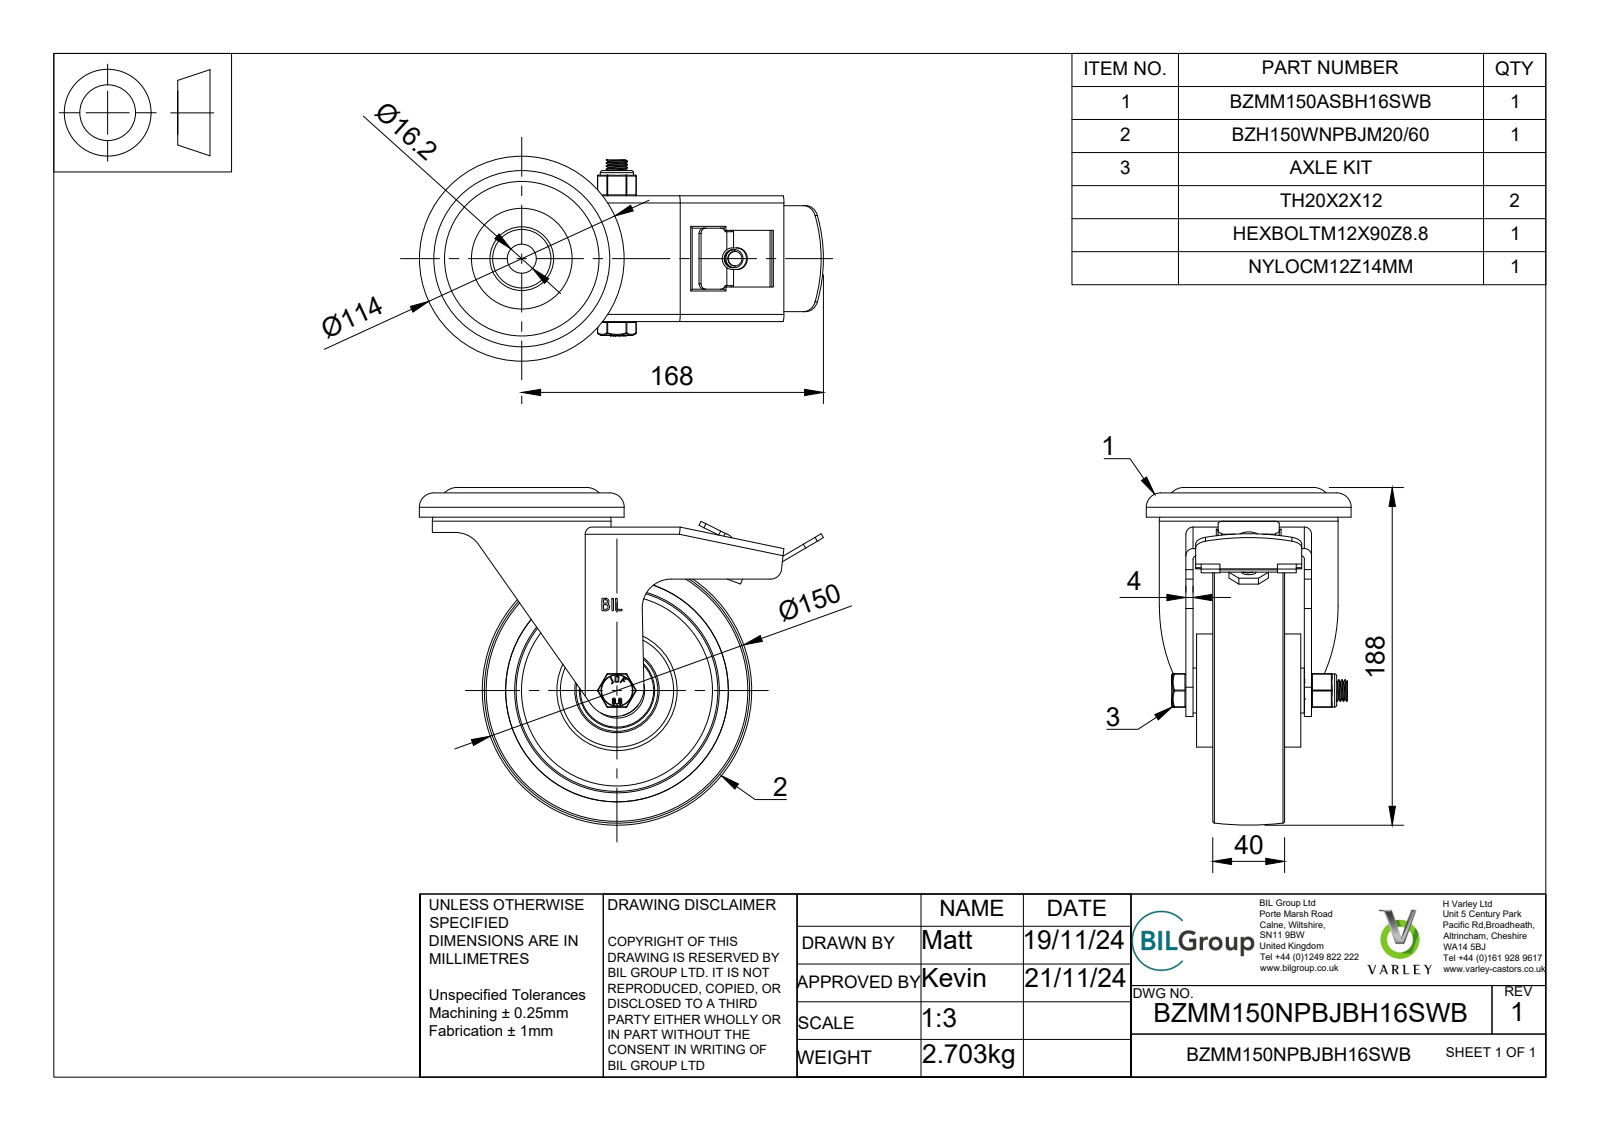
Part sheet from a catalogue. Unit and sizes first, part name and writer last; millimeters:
Units: millimetres
Overall size (bounding box): 225 × 188 × 114
Round holes (diameter × count): ⌀10 ×1, ⌀10.27 ×1, ⌀12 ×1, ⌀12.2 ×1, ⌀14 ×1, ⌀16.2 ×1, ⌀20 ×1, ⌀28.5 ×1, ⌀30.8 ×1, ⌀40.3 ×1, ⌀40.5 ×1, ⌀41 ×1
Round bosses / shafts (diameter × count): ⌀114 ×1, ⌀99.5 ×1, ⌀74 ×1, ⌀63 ×1, ⌀47 ×1, ⌀40.8 ×1, ⌀32.5 ×1, ⌀31.3 ×1
Partial cylindrical surfaces — rounded edges, fillets, slot ends (radius × count): R0.5 ×24, R2 ×8, R1 ×6, R0.47 ×4, R0.9 ×4, R3 ×4, R4 ×4, R6 ×3
Main face-to-face distances: 23.25, 16.75, 4, 27.75, 51, 11, 34.25, 1, 40, 6.5
Volume: 720 730 mm³ · Surface area: 285 703 mm²
Bodies: 40 solids, 1255 faces (558 planar, 254 cylindrical, 443 other)
Part name (STEP PRODUCT): BZMM150NPBJBH16SWB v3; BZMM150ASBH16SWB - 62 v1; ZINC PLATED, PRESSED STEEL HEAD; BRAKE PAD (+8 more)
STEP written by: Autodesk Translation Framework v13.20.0.188 (AP242_MANAGED_MODEL_BASED_3D_ENGINEERING_MIM_LF)
